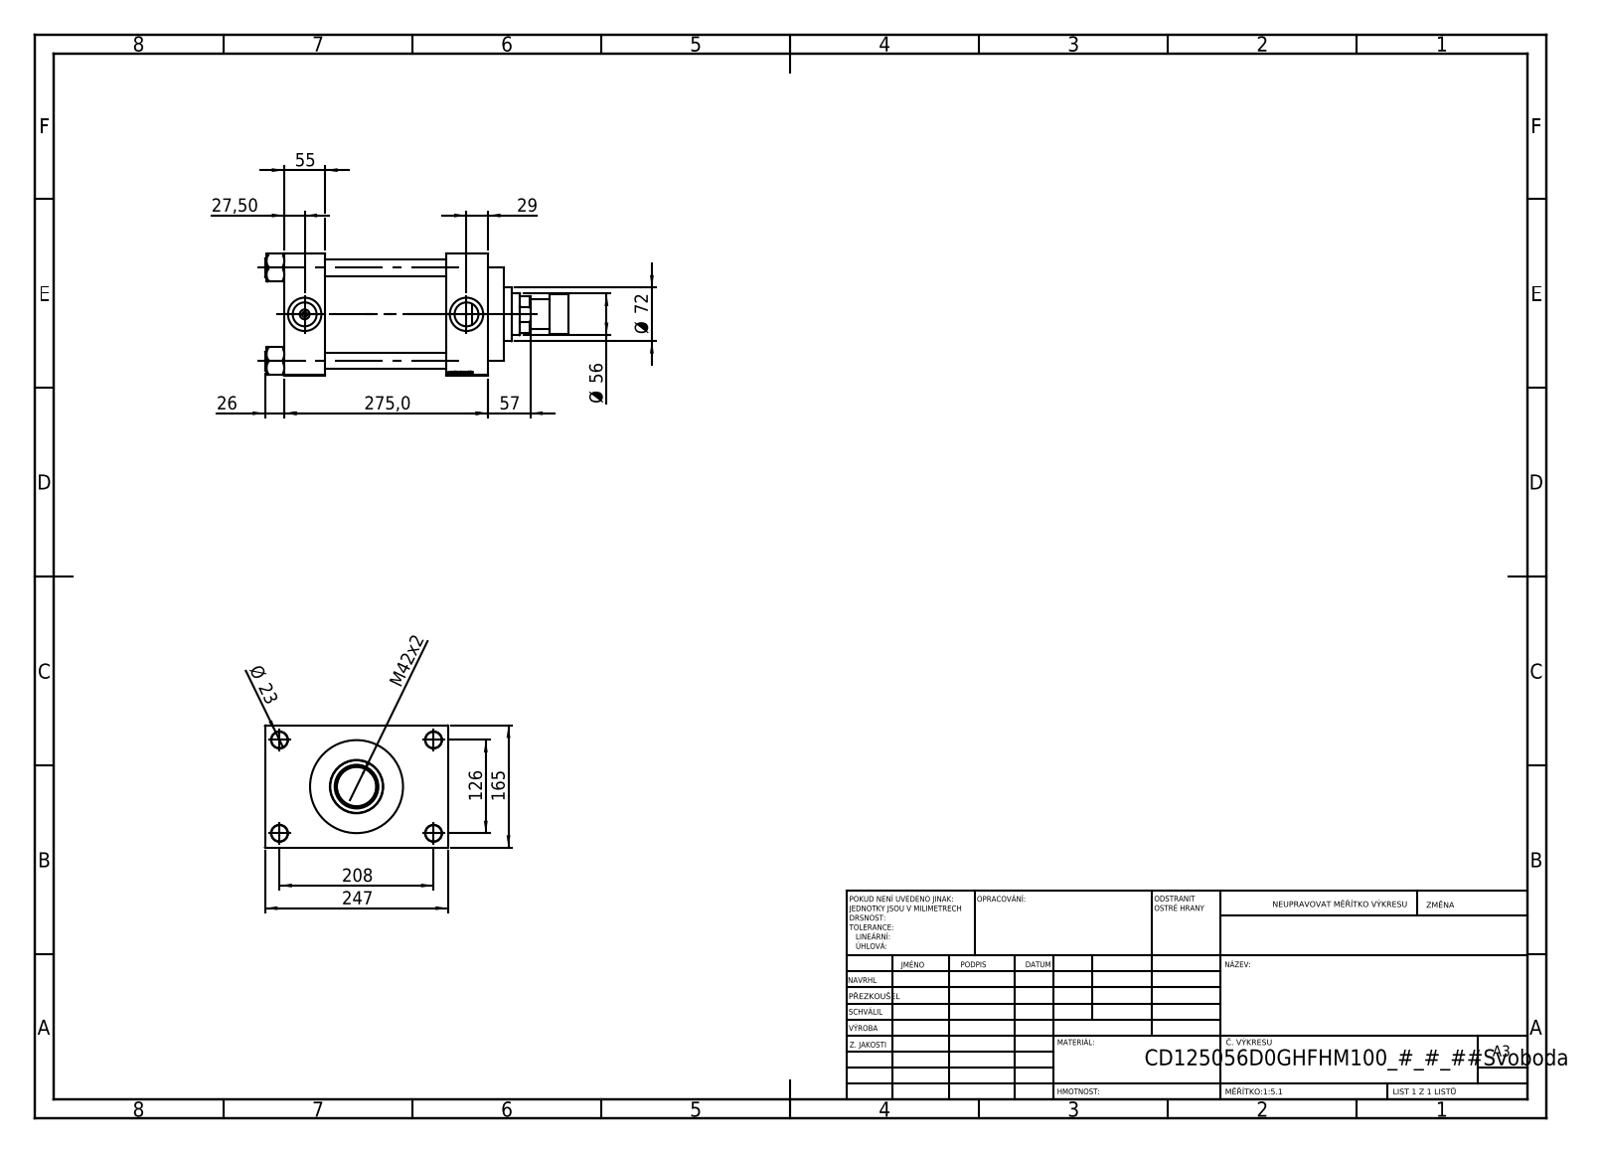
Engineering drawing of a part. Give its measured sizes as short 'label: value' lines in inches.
name: V215CD_D_TYCINKA; V215CD_VCP_D; V215CR_ROD_END_F; V215CD_NUT_M5_D (+2 more)
written by: SolidWorks 2019 (CONFIG_CONTROL_DESIGN)
unit: in
bodies: 12 solids, 1162 faces (548 planar, 90 cylindrical, 524 other)
size: 16.142 × 9.724 × 6.496
volume: 331.5 in³; area: 1 003 in²
holes: 8× ⌀0.866, 2× ⌀0.276, 2× ⌀1.269, 2× ⌀1.772, 1× ⌀1.594, 1× ⌀2.205, 1× ⌀2.323, 1× ⌀3.78, 1× ⌀4.921, 1× ⌀4.941
bosses: 4× ⌀0.984, 1× ⌀5.157, 1× ⌀2.835, 1× ⌀2.126, 1× ⌀1.575
face distances: 6.496, 6.457, 2.165, 8.622, 2.205, 10.827, 8.661, 1.614, 8.11, 9.99
hole spacings: 1.616, 3.505, 4.787, 4.957, 5.215, 6.573, 8.233, 4.961
